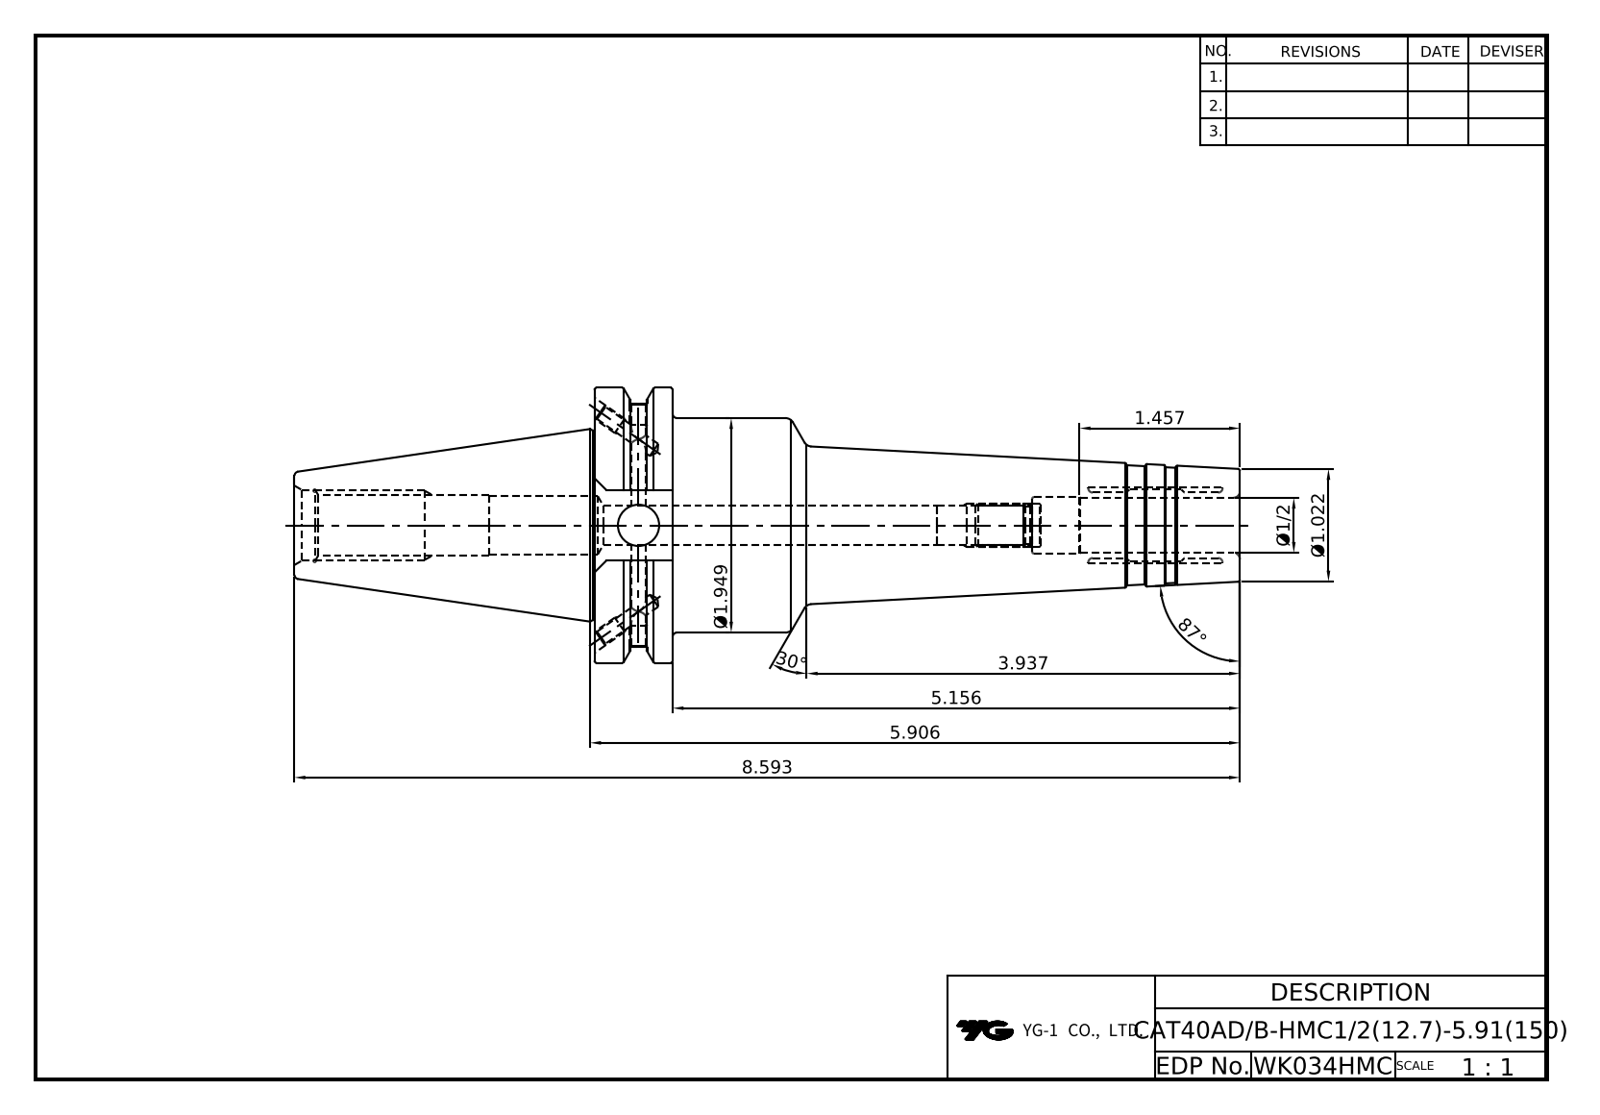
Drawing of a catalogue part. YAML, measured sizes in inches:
part_name: "CAT40ADB-HMC12_7-5_9"
step_written_by: "CREO PARAMETRIC BY PTC INC, 2018500 (CONFIG_CONTROL_DESIGN)"
units: inches
bodies: {solids: 1, faces: 140, planar: 38, cylindrical: 26, other: 76}
overall_size: [8.594, 2.5, 2.395]
volume: 13.77
surface_area: 62.48
round_holes:
  - {diameter: 0.354, count: 1}
  - {diameter: 0.375, count: 1}
  - {diameter: 0.394, count: 1}
  - {diameter: 0.5, count: 1}
  - {diameter: 0.52, count: 1}
  - {diameter: 0.531, count: 1}
  - {diameter: 0.625, count: 1}
  - {diameter: 0.642, count: 1}
round_bosses_or_shafts:
  - {diameter: 2.5, count: 1}
  - {diameter: 2.217, count: 1}
  - {diameter: 1.949, count: 1}
  - {diameter: 1.717, count: 1}
face_to_face_distances: [0.626, 5.782, 5.156, 1.874, 2.812, 3.438, 8.594, 0.645, 3.05, 0.238]
